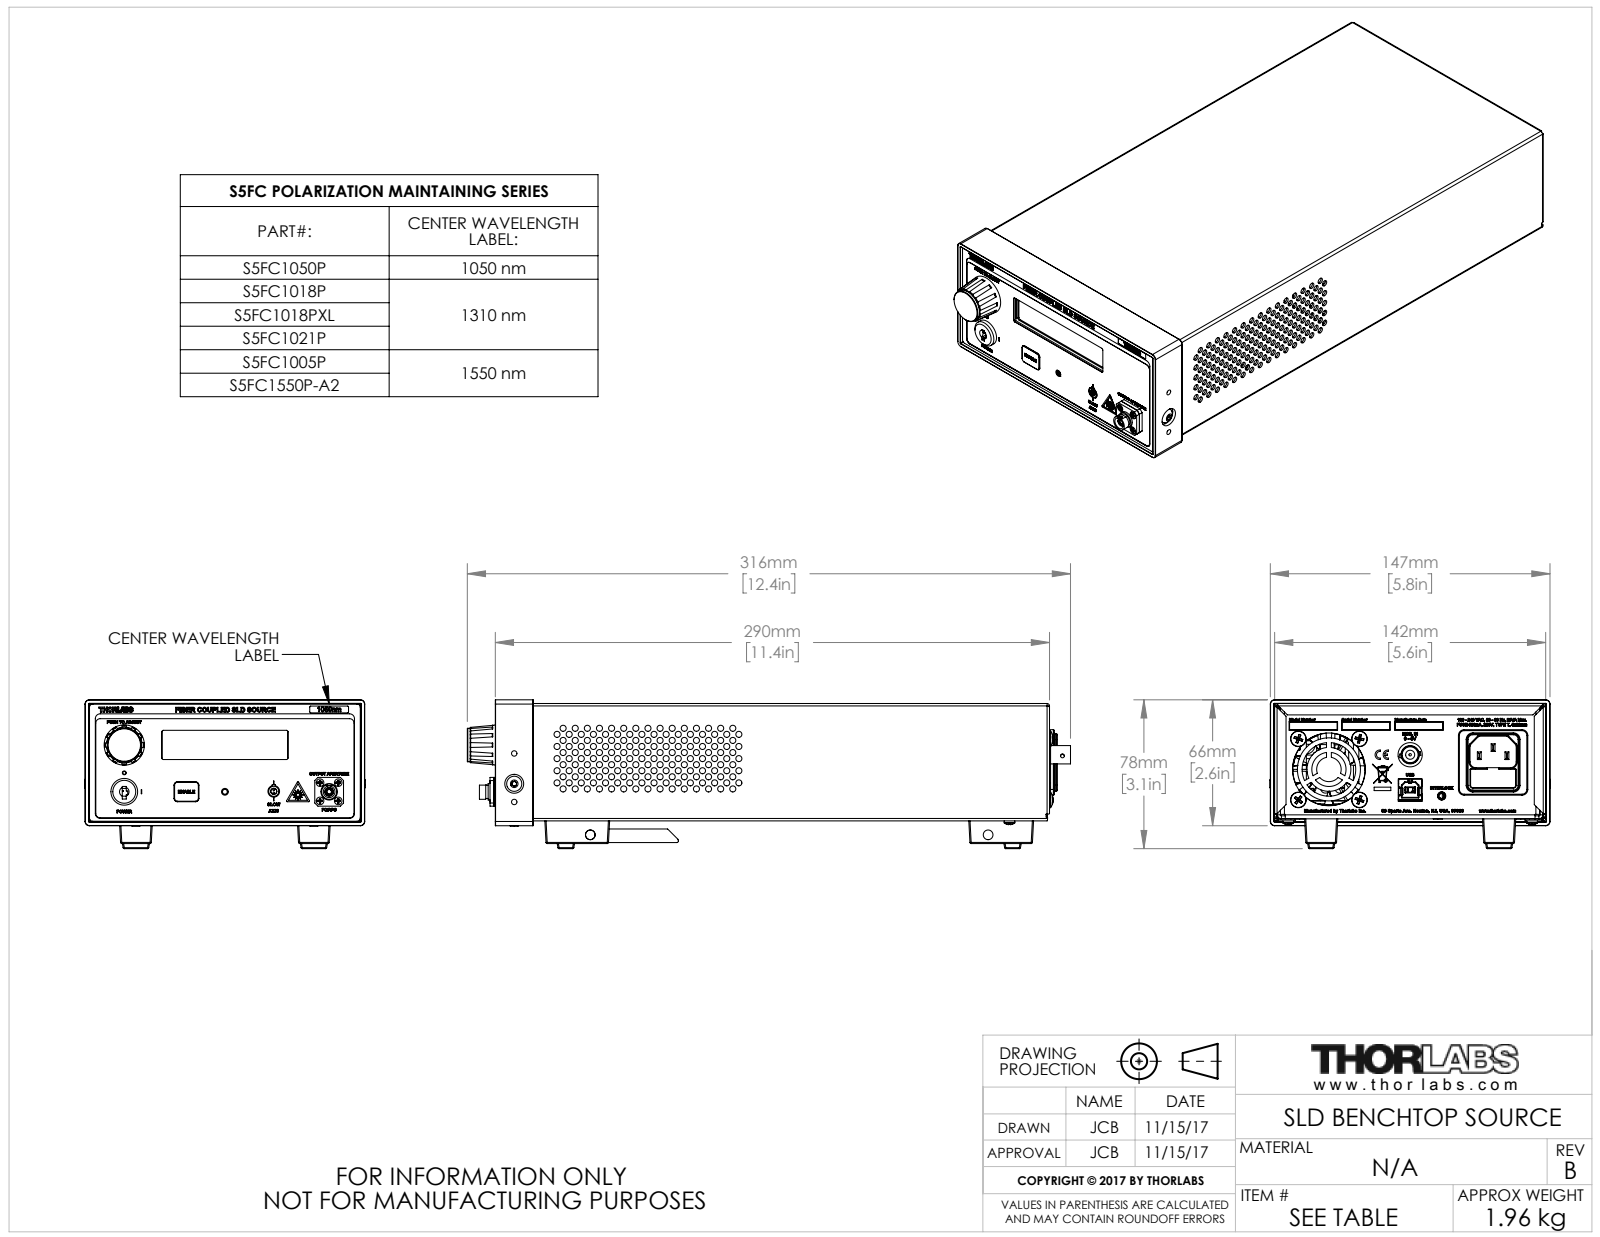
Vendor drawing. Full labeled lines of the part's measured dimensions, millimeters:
Part name (STEP PRODUCT): 19844-E0W
STEP written by: SolidWorks 2016 (AUTOMOTIVE_DESIGN)
Units: millimetres
Bodies: 0 solids, 12621 faces (7394 planar, 2810 cylindrical, 2417 other)
Overall size (bounding box): 316 × 147 × 78
Round holes (diameter × count): ⌀3.2 ×170, ⌀0.9 ×79, ⌀1 ×46, ⌀1 ×16, ⌀0.8 ×14, ⌀2.5 ×12, ⌀3 ×9, ⌀3.7 ×9, ⌀1.8 ×8, ⌀2.2 ×8, ⌀2.2 ×8, ⌀2.8 ×8
Round bosses / shafts (diameter × count): ⌀0.8 ×16, ⌀4.2 ×12, ⌀4.1 ×12, ⌀3.9 ×12, ⌀4.2 ×9, ⌀3 ×8, ⌀0.5 ×6, ⌀7.9 ×5
Partial cylindrical surfaces — rounded edges, fillets, slot ends (radius × count): R0.5 ×77, R0.6 ×52, R0.2 ×39, R0.1 ×32, R0.3 ×20, R1.3 ×17, R0.2 ×16, R0.3 ×15
Main face-to-face distances: 1.6, 1, 7.8, 60.4, 59.4, 57.8, 58.8, 9.4, 49.9, 51
Hole centre spacings: 5.1, 6.7, 9.5, 20.3, 10.2, 24.7, 2.5, 4.1
